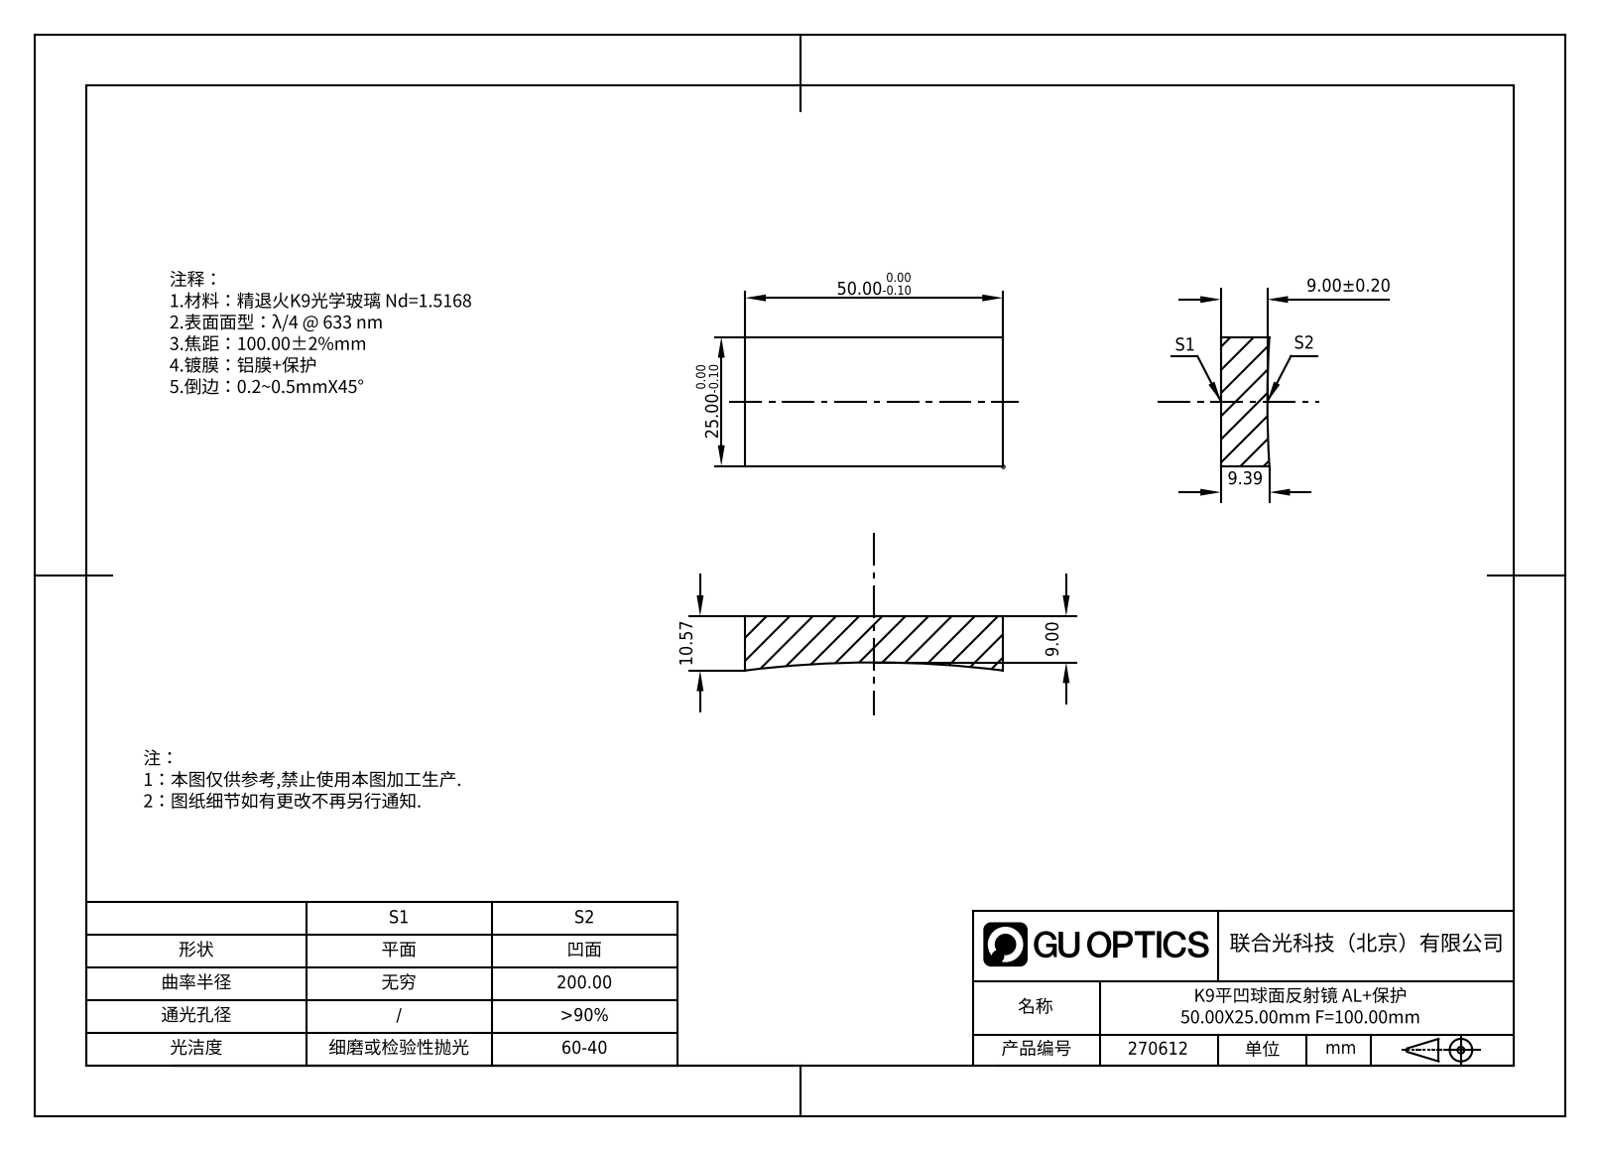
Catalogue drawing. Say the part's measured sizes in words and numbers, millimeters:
The part is named "GM13-50x25-100". Its 3-D file was written by "SolidWorks 2022 (AUTOMOTIVE_DESIGN)". It is 1 solid with 7 faces: 5 planar, 0 cylindrical and 2 other. Overall it measures 50 by 25 by 10.96 millimeters. Its volume is 12 066 cubic millimeters and its surface area 4 031 square millimeters. The main face-to-face distances are 25, 50.
